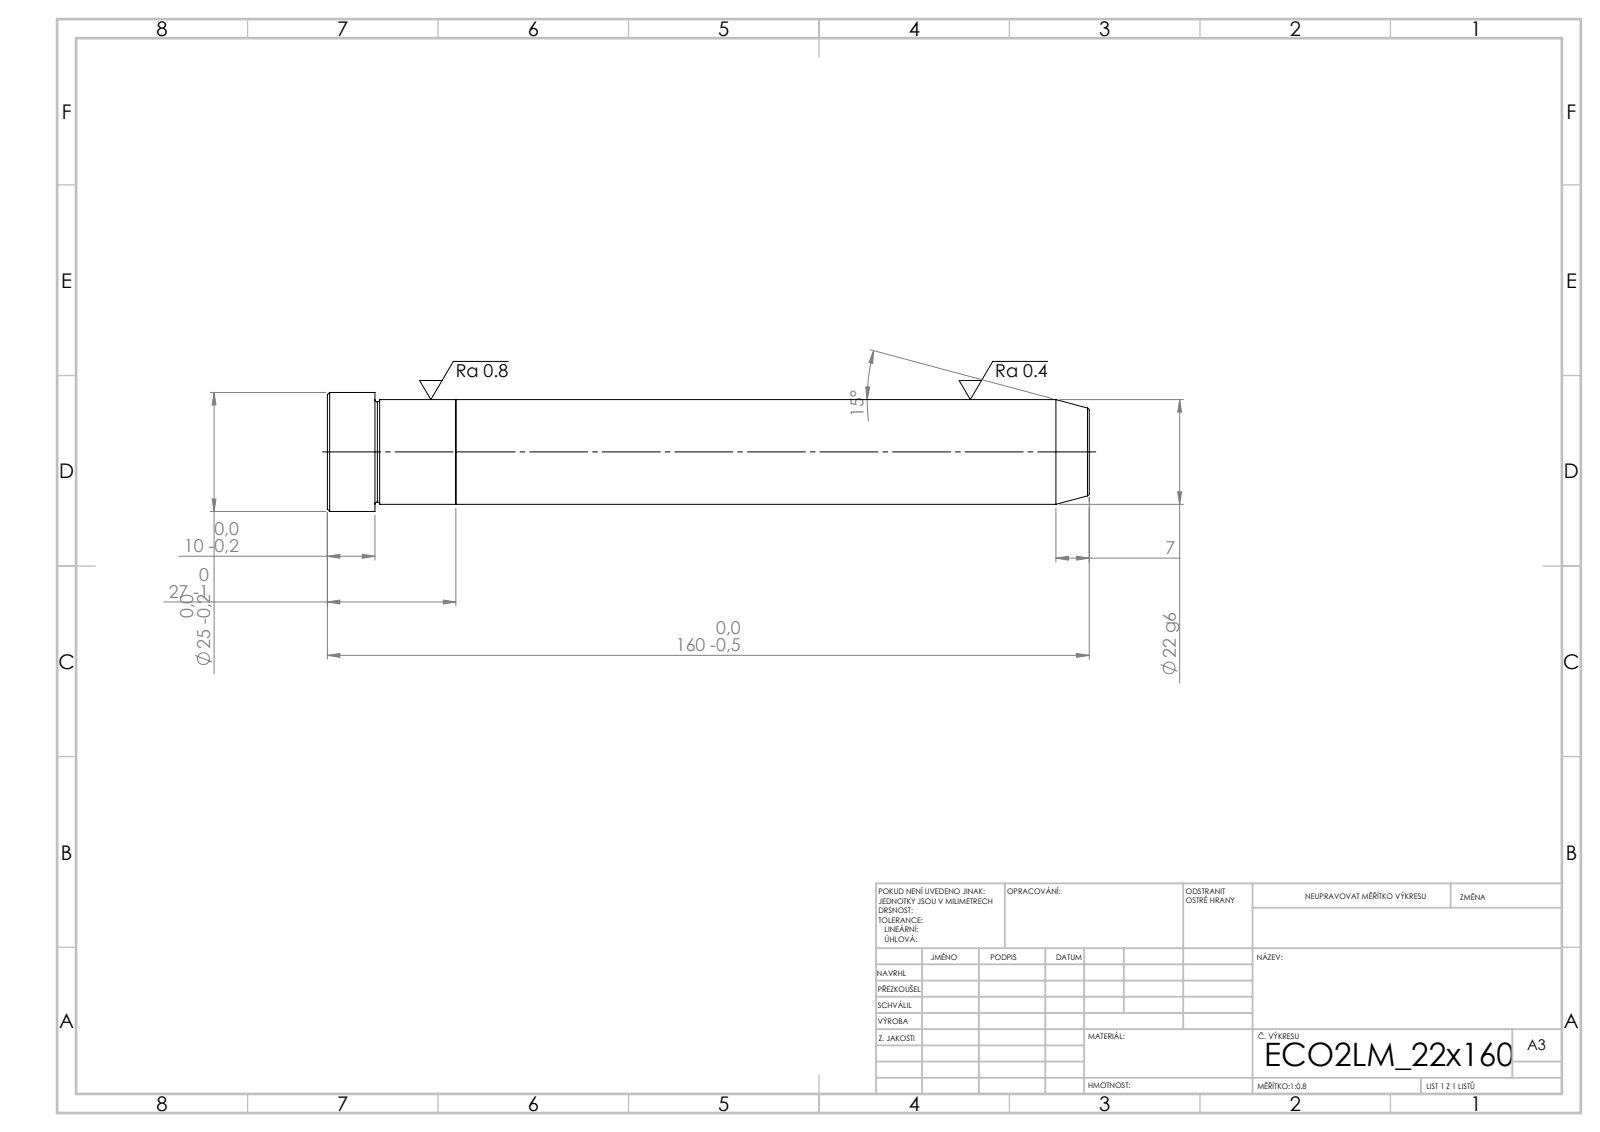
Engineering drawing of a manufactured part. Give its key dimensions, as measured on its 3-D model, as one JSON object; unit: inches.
{"step_written_by": "SolidWorks 2019 (CONFIG_CONTROL_DESIGN)", "units": "inches", "bodies": {"solids": 2, "faces": 21, "planar": 5, "cylindrical": 6, "other": 10}, "overall_size": [6.299, 0.984, 0.984], "volume_in3": 3.751, "surface_area_in2": 19.77, "round_bosses_or_shafts": [[0.984, 1], [0.866, 1]], "face_to_face_distances": [1.063, 5.236, 6.299, 5.906, 0.669, 0.394]}
